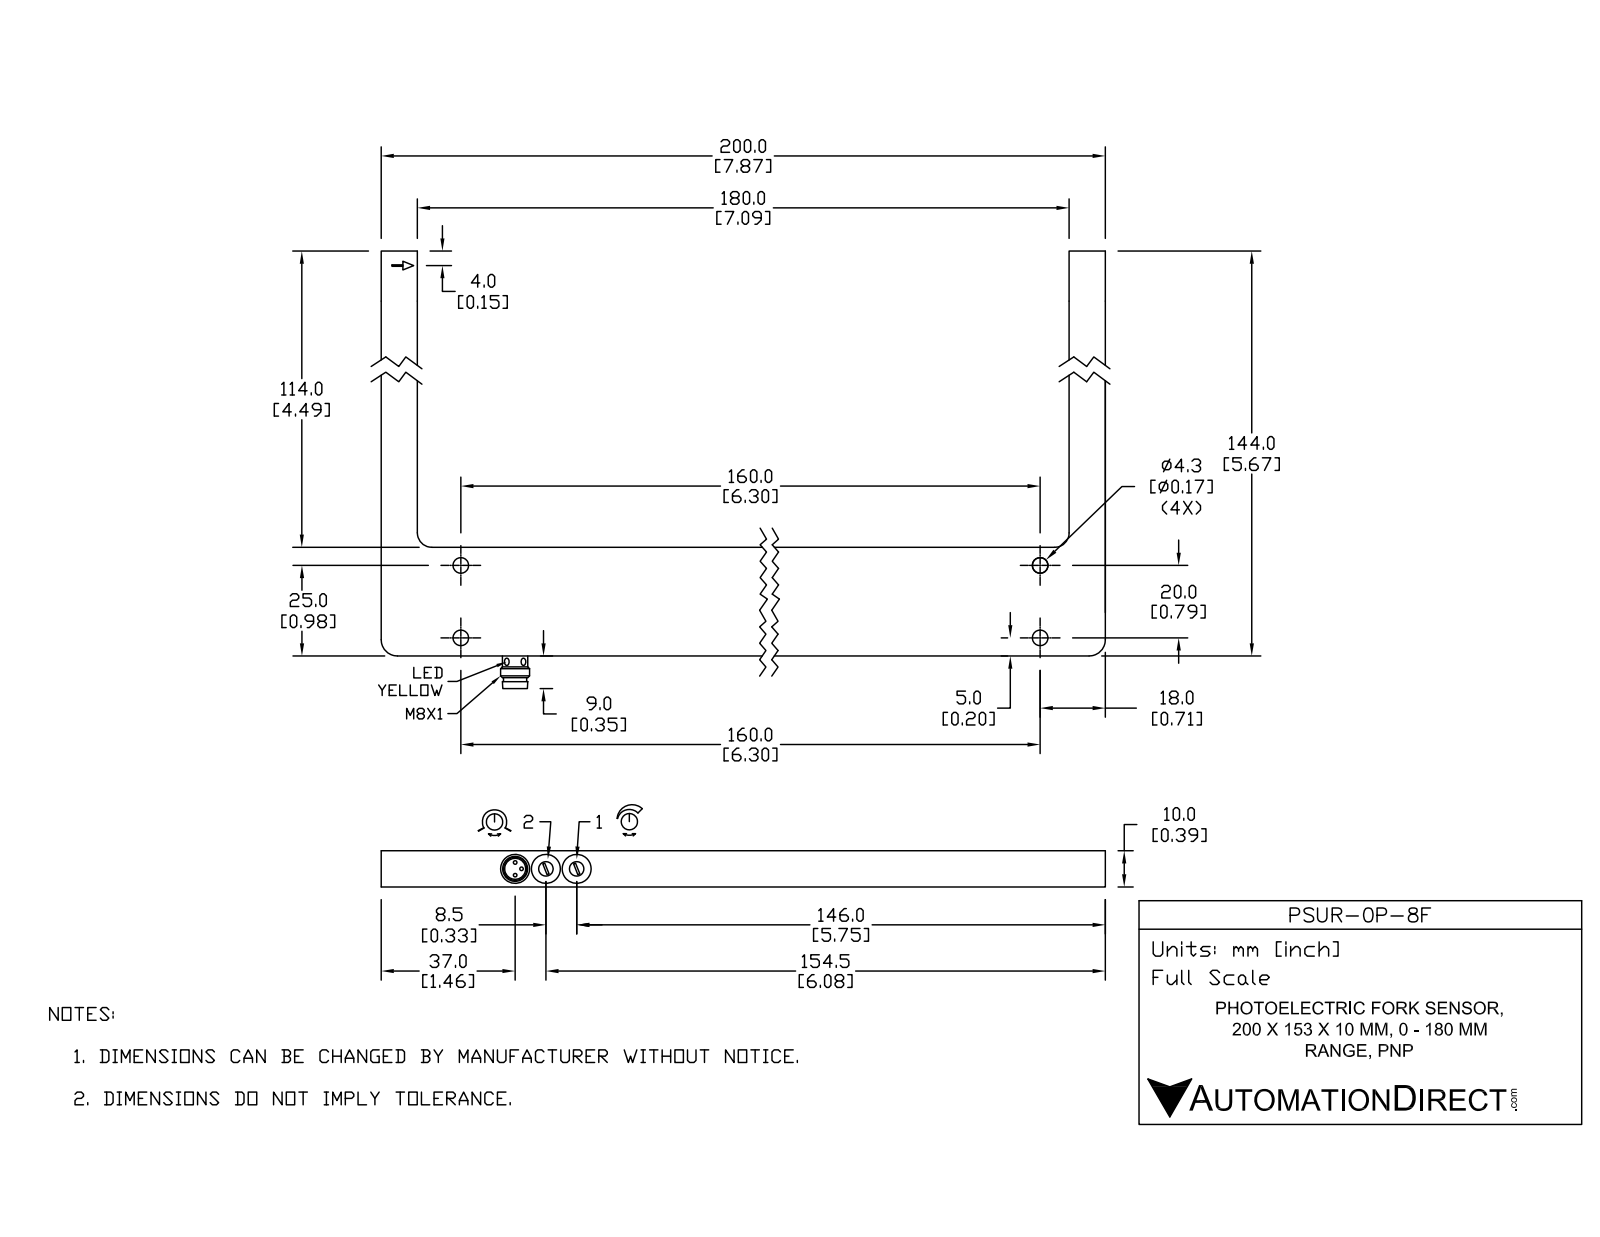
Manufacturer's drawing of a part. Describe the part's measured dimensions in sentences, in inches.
The part is named "PSUR-0P-8F". Its 3-D file was written by "SolidWorks 2016 (AUTOMOTIVE_DESIGN)". It is 1 solid with 81 faces: 35 planar, 40 cylindrical and 6 other. Overall it measures 7.874 by 6.024 by 0.394 inches. Its volume is 5.027 cubic inches and its surface area 40.91 square inches. Round holes: 4 of diameter 0.169, 2 of diameter 0.079, 2 of diameter 0.157, 2 of diameter 0.315, 1 of diameter 0.228. Round bosses or shafts: 1 of diameter 0.315, 1 of diameter 0.267. Partial cylindrical surfaces (rounded edges, fillets, slot ends): 2 of radius 0.063, 2 of radius 0.157, 2 of radius 0.197. The main face-to-face distances are 0.394, 7.48, 1.181, 7.874, 7.087, 4.488, 5.669, 5.665, 1.177, 0.157. The hole center spacings are 0.335, 0.787, 6.299, 6.348, 0.669.
